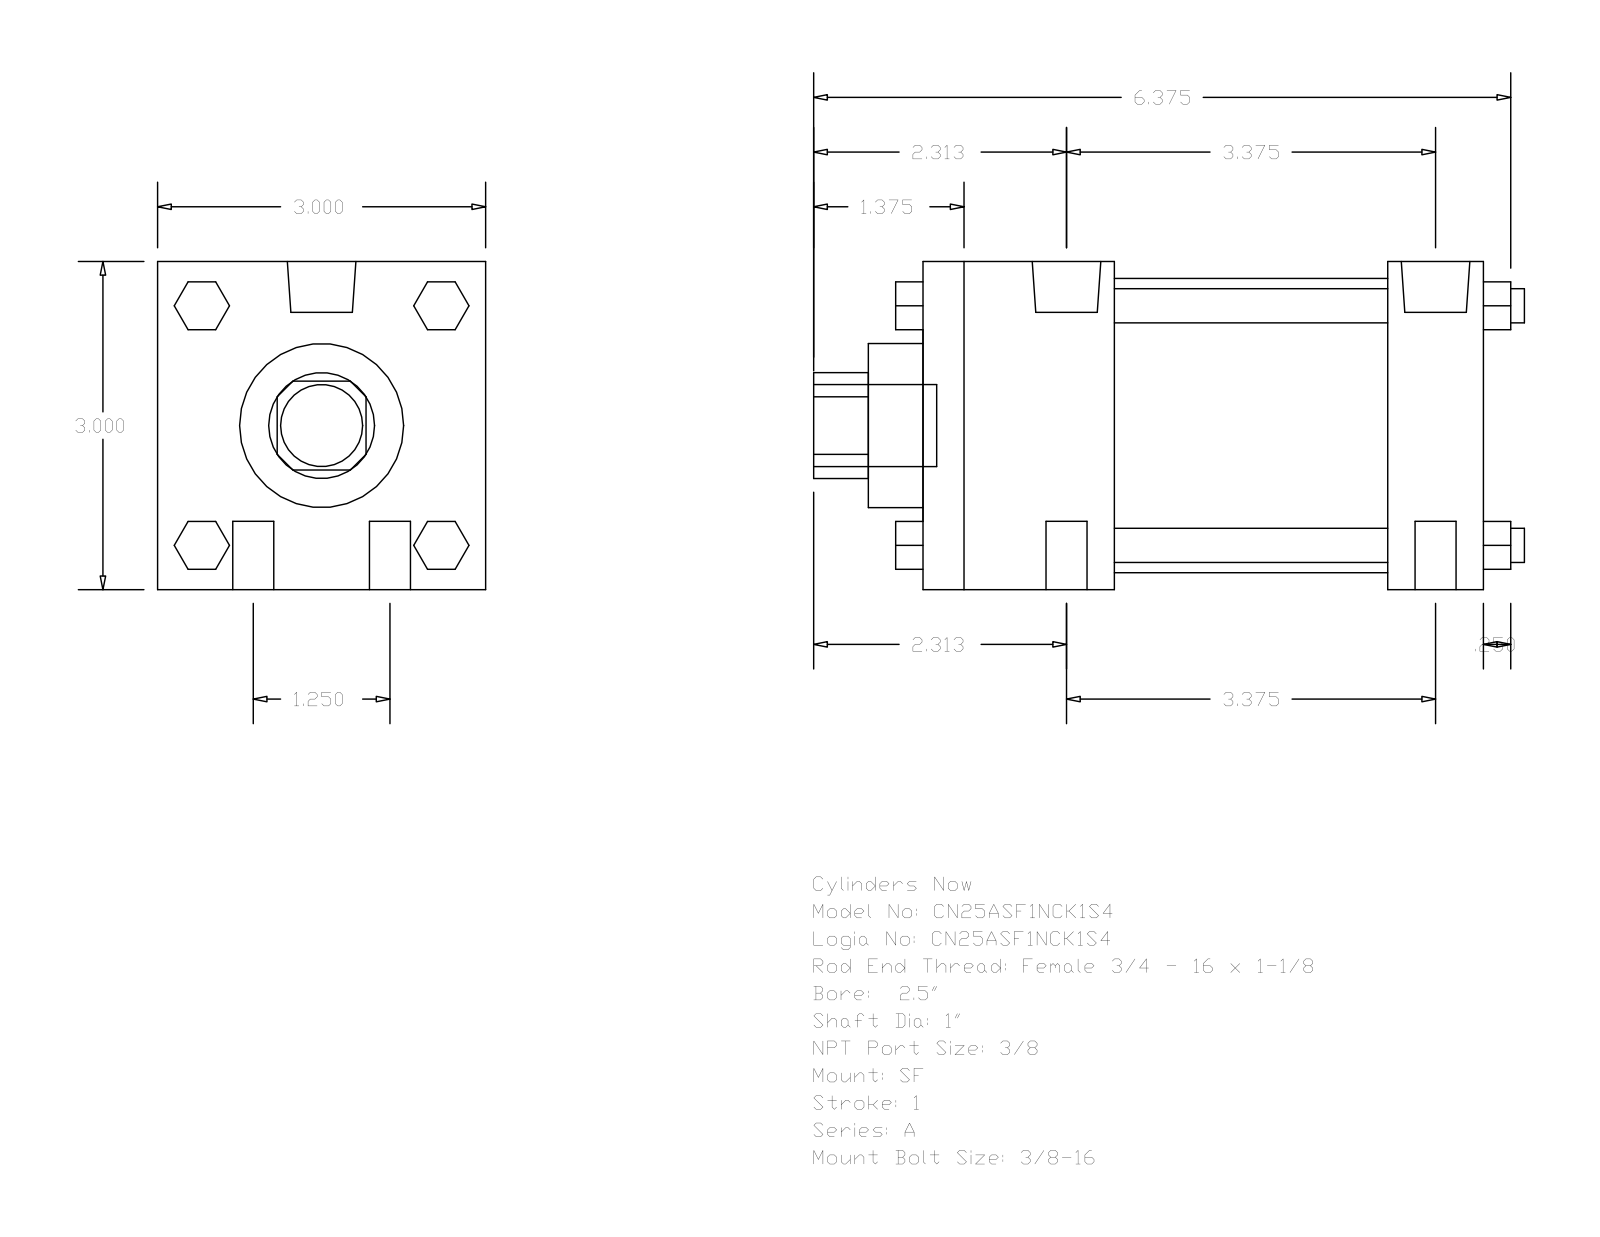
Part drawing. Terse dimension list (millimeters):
name: A_SF__0250_1
written by: GSSL Pune (CONFIG_CONTROL_DESIGN)
unit: mm
bodies: 0 solids, 124 faces (94 planar, 30 cylindrical, 0 other)
size: 165.1 × 76.2 × 76.2
holes: 1× ⌀25.4, 1× ⌀38.1, 1× ⌀68.33
bosses: 4× ⌀9.53, 4× ⌀7.94, 2× ⌀15.93, 2× ⌀5.56, 1× ⌀19.05
rounds: 1× R12.29
face distances: 76.2, 130.17, 63.5, 107.95, 22.22, 44.45, 85.72, 12.7, 11.11, 57.15
